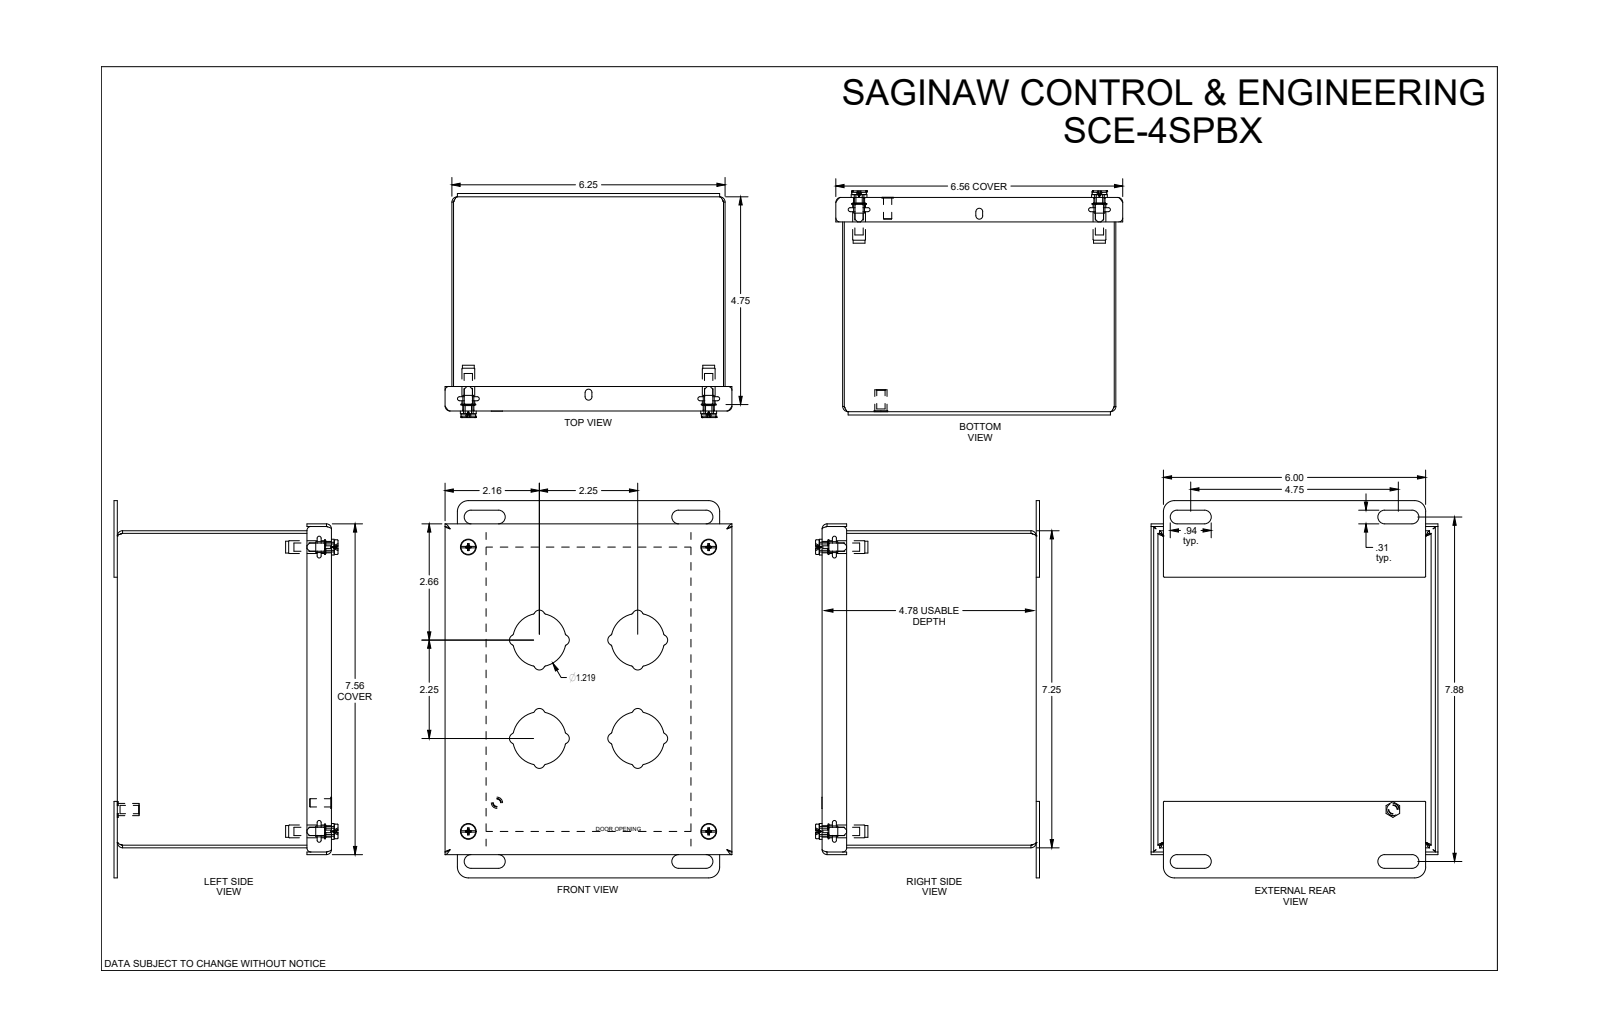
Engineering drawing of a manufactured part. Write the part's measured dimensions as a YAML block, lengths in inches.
part_name: "SCE-4SPBX"
step_written_by: "SolidWorks 2021 (AUTOMOTIVE_DESIGN)"
units: inches
bodies: {solids: 3, faces: 475, planar: 154, cylindrical: 237, other: 84}
overall_size: [8.625, 6.563, 5.036]
volume: 16.42
surface_area: 519.1
round_holes:
  - {diameter: 0.19, count: 5}
  - {diameter: 0.22, count: 4}
  - {diameter: 0.25, count: 4}
  - {diameter: 0.266, count: 4}
  - {diameter: 0.317, count: 4}
round_bosses_or_shafts:
  - {diameter: 0.362, count: 4}
  - {diameter: 0.34, count: 4}
  - {diameter: 0.292, count: 4}
  - {diameter: 0.27, count: 4}
  - {diameter: 0.26, count: 4}
  - {diameter: 0.28, count: 1}
  - {diameter: 0.256, count: 1}
  - {diameter: 0.188, count: 1}
partial_cylinders:
  - {radius: 0.04, count: 32}
  - {radius: 0.06, count: 20}
  - {radius: 0.125, count: 16}
  - {radius: 0.015, count: 8}
  - {radius: 0.115, count: 8}
  - {radius: 0.156, count: 8}
  - {radius: 0.245, count: 8}
  - {radius: 0.02, count: 4}
face_to_face_distances: [0.06, 4.838, 6.19, 7.19, 4.778, 4.898, 6.25, 6.13, 7.25, 7.13]
hole_center_spacings: [8.515, 5.5, 5.5, 6.5, 6.5, 5.024, 5.495, 6.021]
